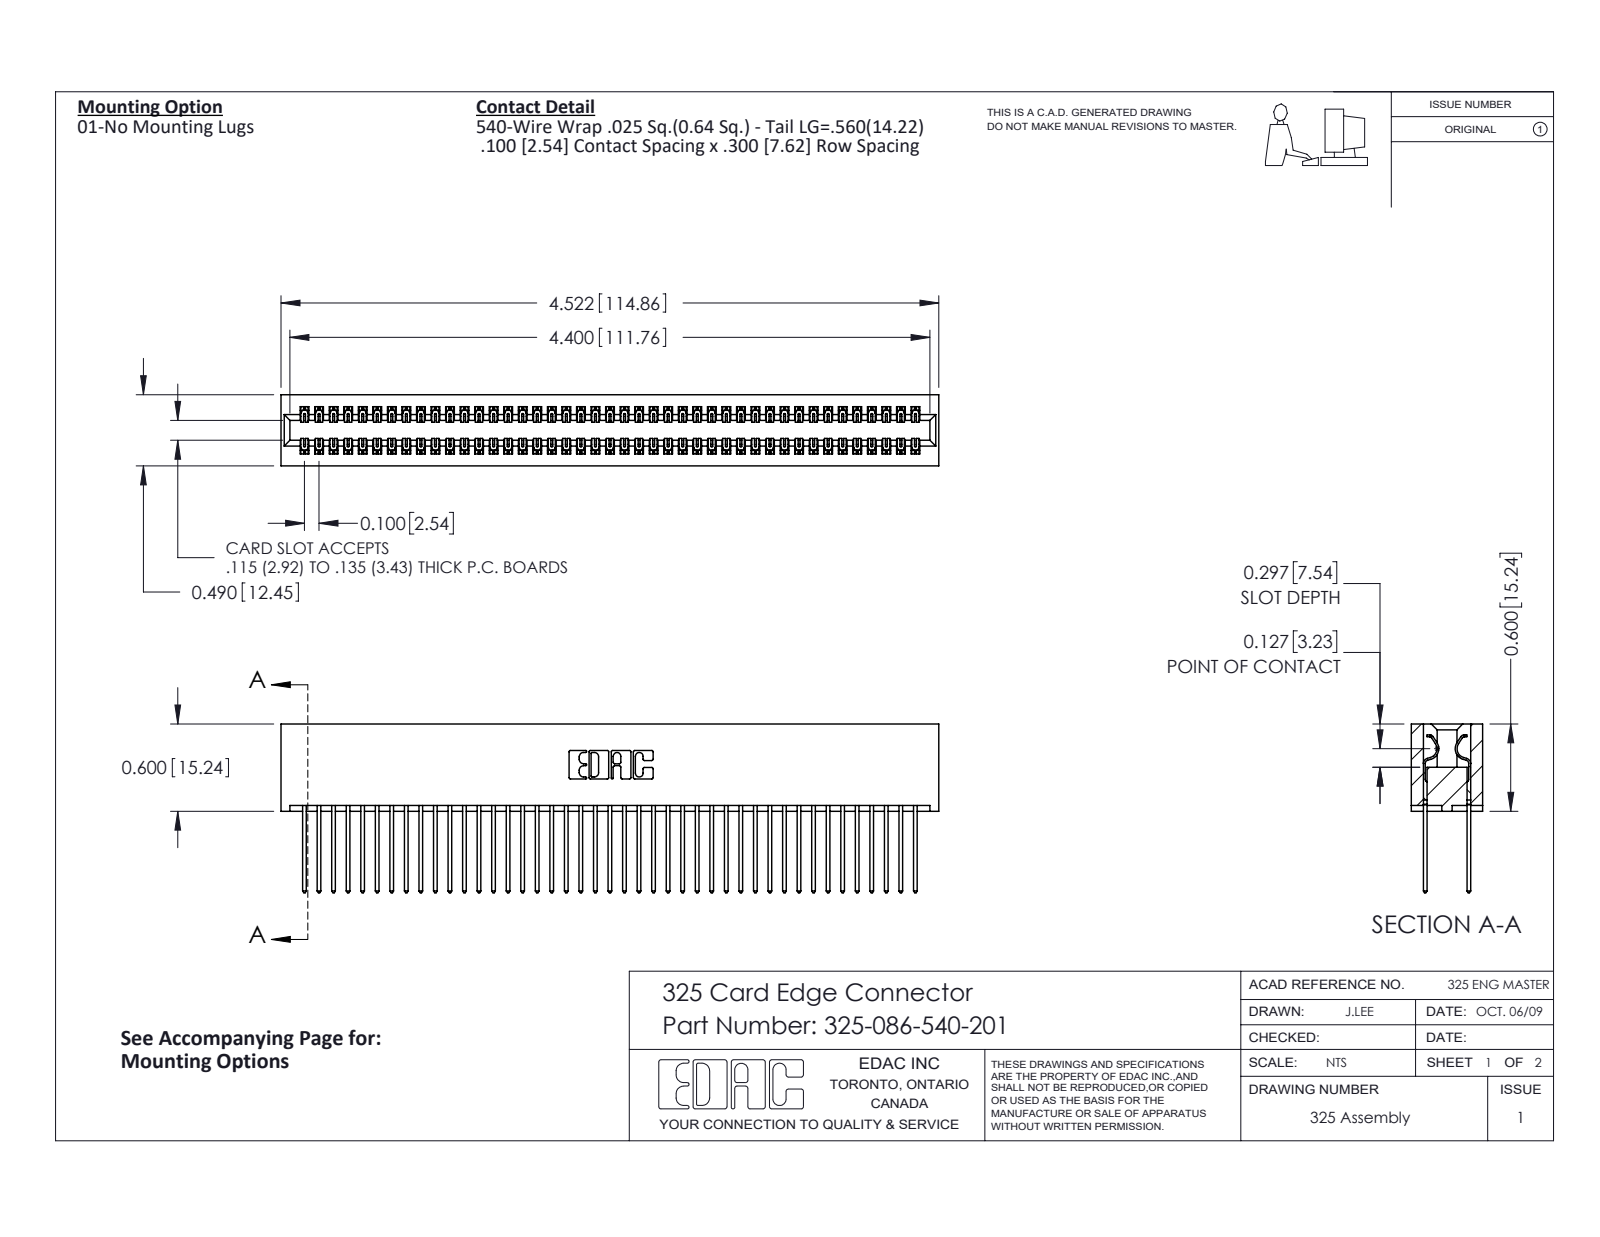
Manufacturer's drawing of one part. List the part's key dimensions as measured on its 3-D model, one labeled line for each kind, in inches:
Part name (STEP PRODUCT): 325-292-001_325-293-140; 325 Part_Lugless; 325-086-540-201
STEP written by: SolidWorks 2016 (CONFIG_CONTROL_DESIGN)
Units: inches
Bodies: 87 solids, 4578 faces (3162 planar, 1416 cylindrical, 0 other)
Overall size (bounding box): 4.522 × 1.16 × 0.49
Volume: 0.962 in³ · Surface area: 33.05 in²
Partial cylindrical surfaces — rounded edges, fillets, slot ends (radius × count): R0.006 ×129, R0.01 ×86, R0.01 ×22, R0.007 ×6, R0.031 ×6, R0.026 ×3, R0.014 ×2, R0.022 ×2
Main face-to-face distances: 0.083, 0.407, 0.3, 0.107, 0.383, 0.025, 0.325, 0.49, 0.275, 0.56
